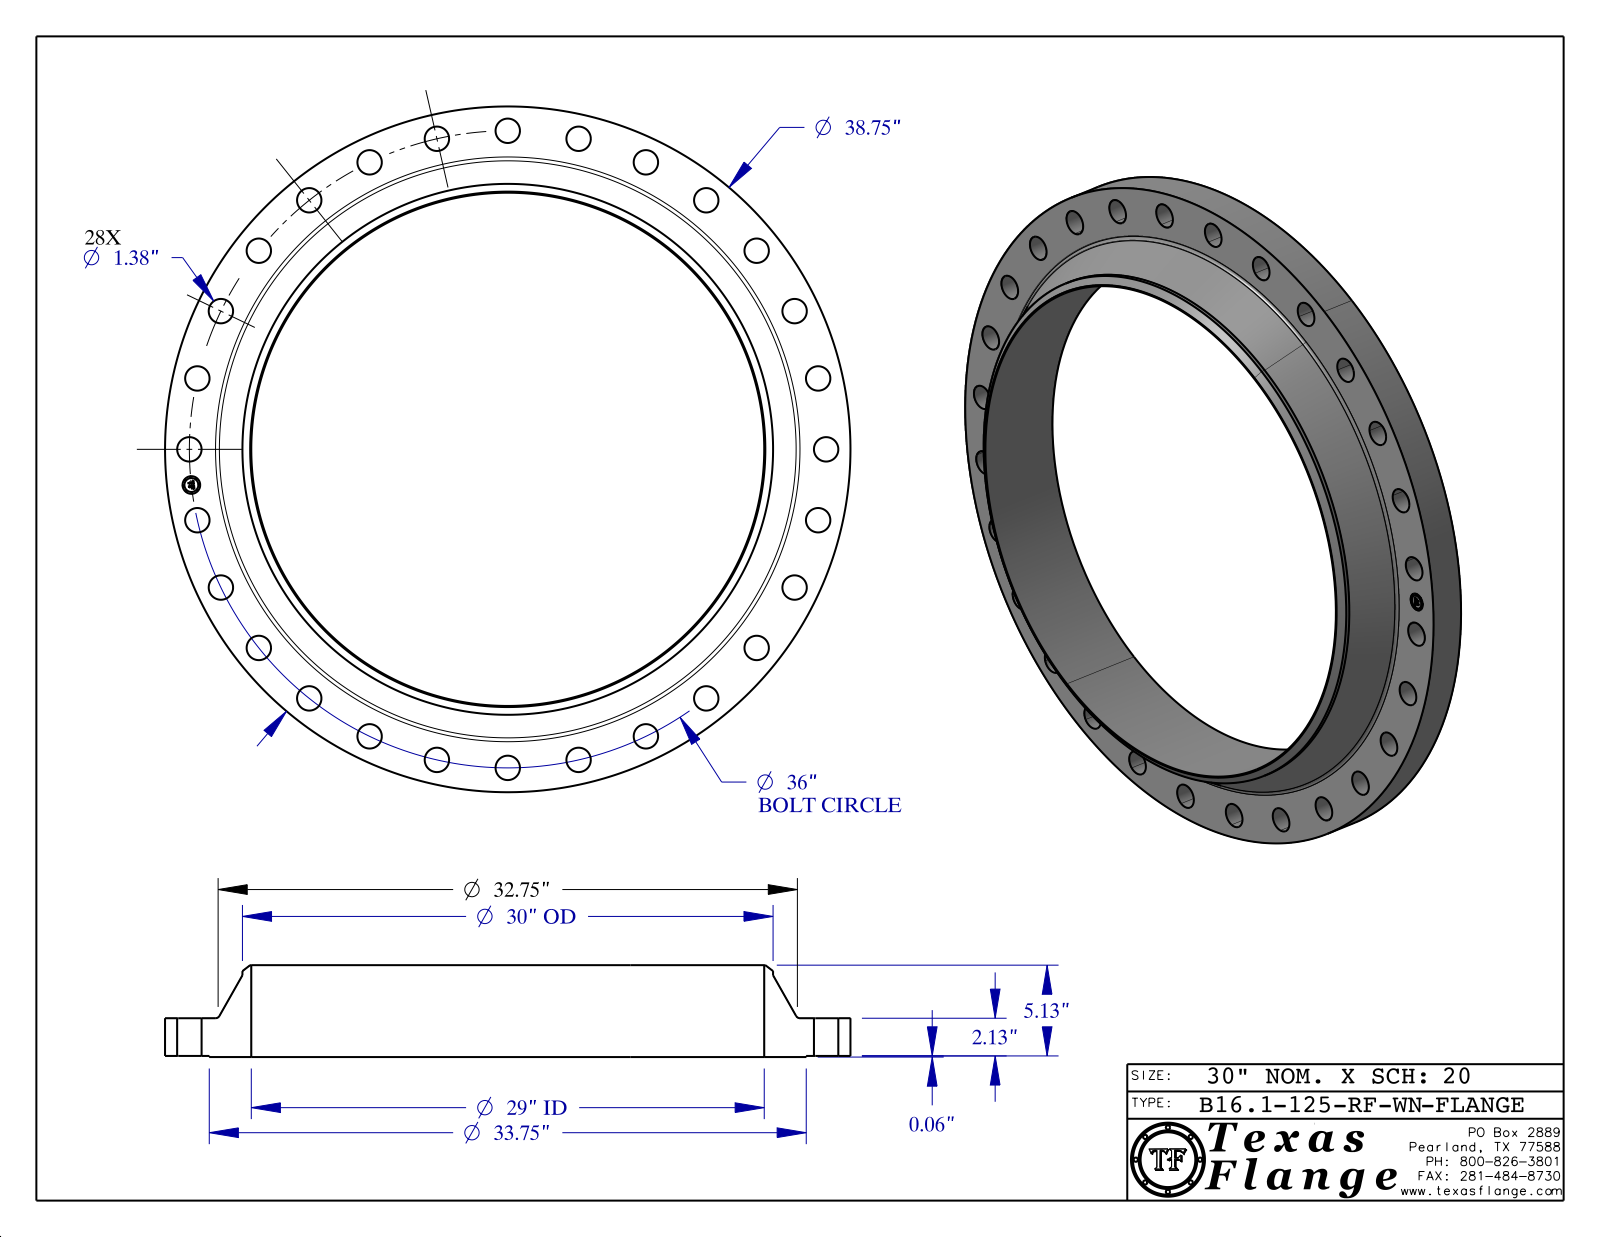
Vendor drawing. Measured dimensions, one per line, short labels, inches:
name: B16.1, Class 125-RF-WN
written by: CATIA V5 STEP AP214 (AUTOMOTIVE_DESIGN)
unit: in
bodies: 1 solid, 459 faces (369 planar, 84 cylindrical, 6 other)
size: 38.75 × 38.75 × 5.193
volume: 1 325 in³; area: 2 121 in²
holes: 28× ⌀1.38, 1× ⌀1, 1× ⌀29
bosses: 8× ⌀0.061, 1× ⌀38.75, 1× ⌀33.75, 1× ⌀30, 1× ⌀0.788
face distances: 2.13, 0.063, 2.193, 5.193, 5.13, 3, 0.015, 2.178, 2.115, 3.015
hole spacings: 18, 19.153, 4.031, 8.011, 11.89, 15.62, 22.446, 25.456
